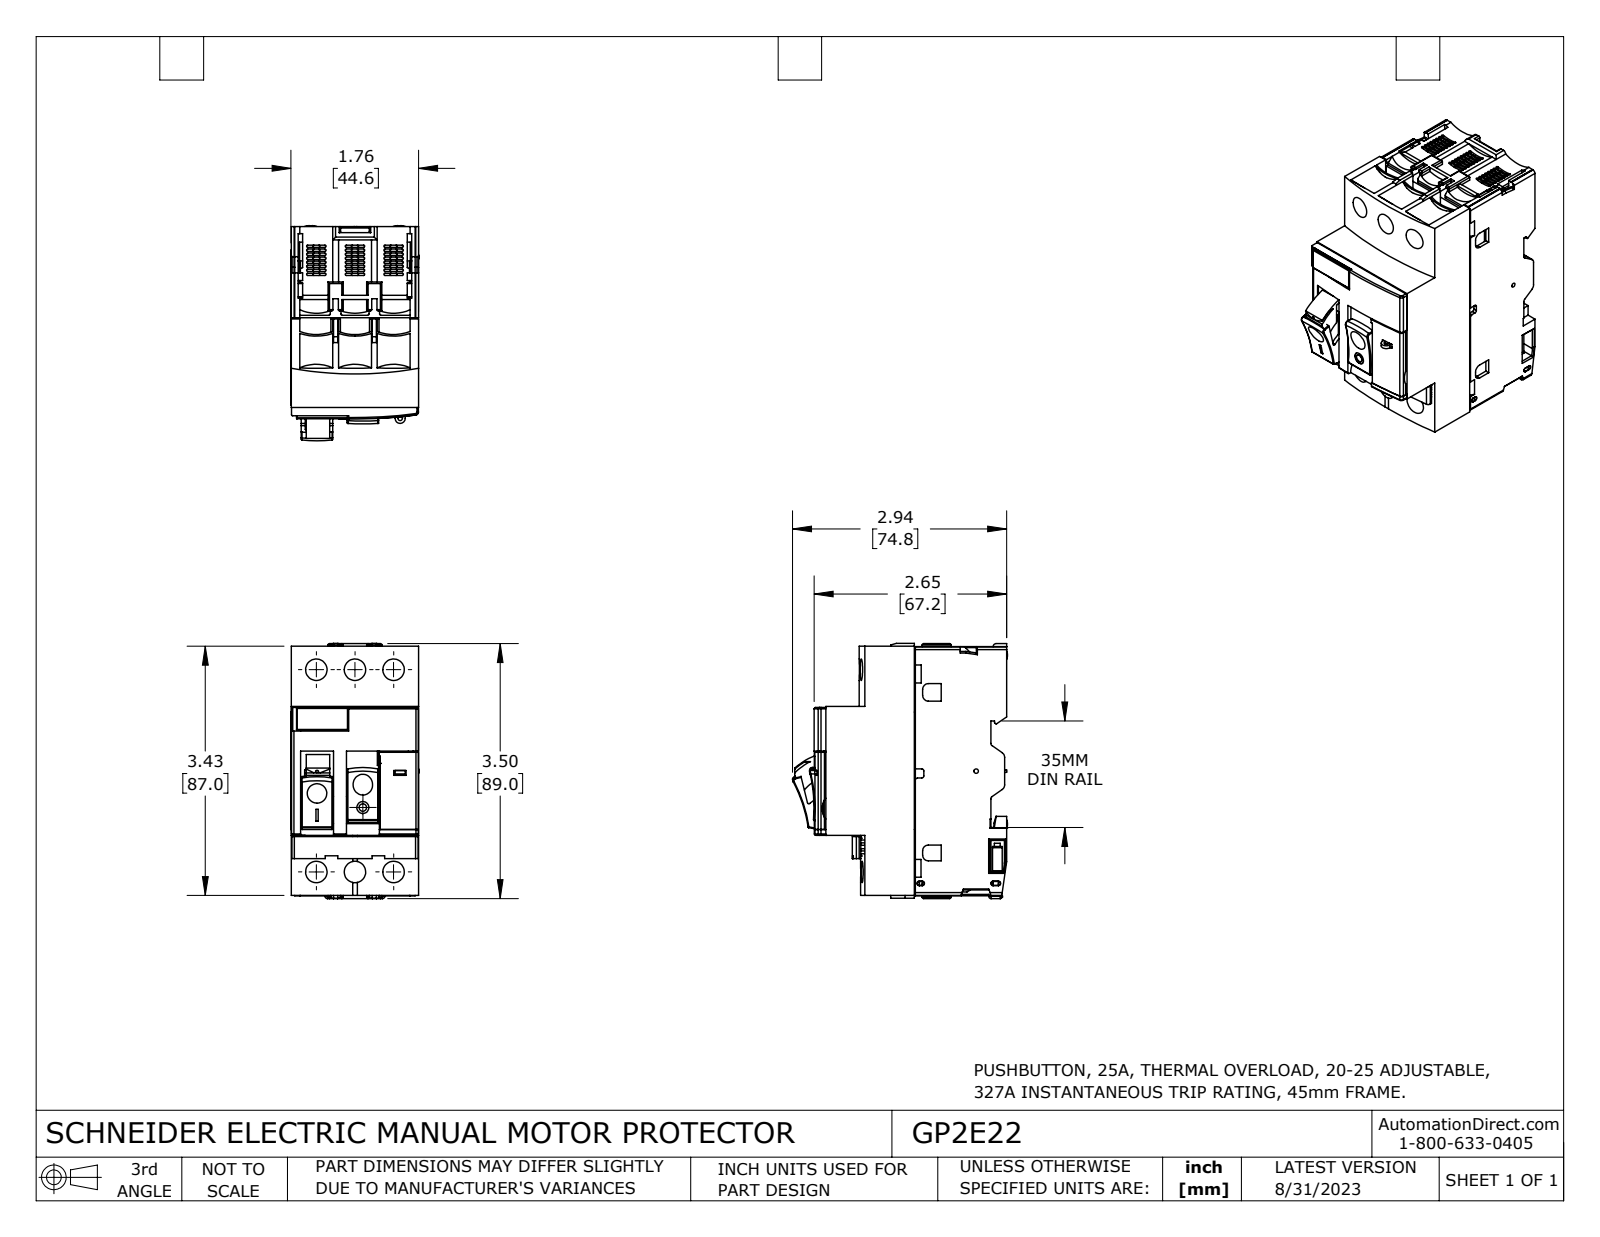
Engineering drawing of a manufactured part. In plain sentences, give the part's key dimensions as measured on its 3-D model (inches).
The part is named "GP2E22". Its 3-D file was written by "SolidWorks 2021 (CONFIG_CONTROL_DESIGN)". It is 15 solids with 2269 faces: 1521 planar, 657 cylindrical and 91 other. Overall it measures 3.508 by 2.957 by 1.764 inches. Its volume is 11.58 cubic inches and its surface area 98.93 square inches. Round holes: 6 of diameter 0.295, 5 of diameter 0.197, 2 of diameter 0.059, 1 of diameter 0.157, 1 of diameter 0.165, 1 of diameter 0.315, 1 of diameter 0.327, 1 of diameter 0.335, 1 of diameter 0.343. Round bosses or shafts: 2 of diameter 0.244, 2 of diameter 0.118, 1 of diameter 0.382, 1 of diameter 0.102, 1 of diameter 0.047. Partial cylindrical surfaces (rounded edges, fillets, slot ends): 104 of radius 0.016, 47 of radius 0.02, 16 of radius 0.039, 12 of radius 0.01, 12 of radius 0.012, 12 of radius 0.031, 8 of radius 0.059, 6 of radius 0.004. The main face-to-face distances are 1.752, 0.531, 0.115, 1.233, 1.756, 0.059, 1.637, 0.581, 1.053, 1.171. The hole center spacings are 0.531, 2.83, 2.779, 0.346, 0.402, 0.546, 0.671, 0.726.
